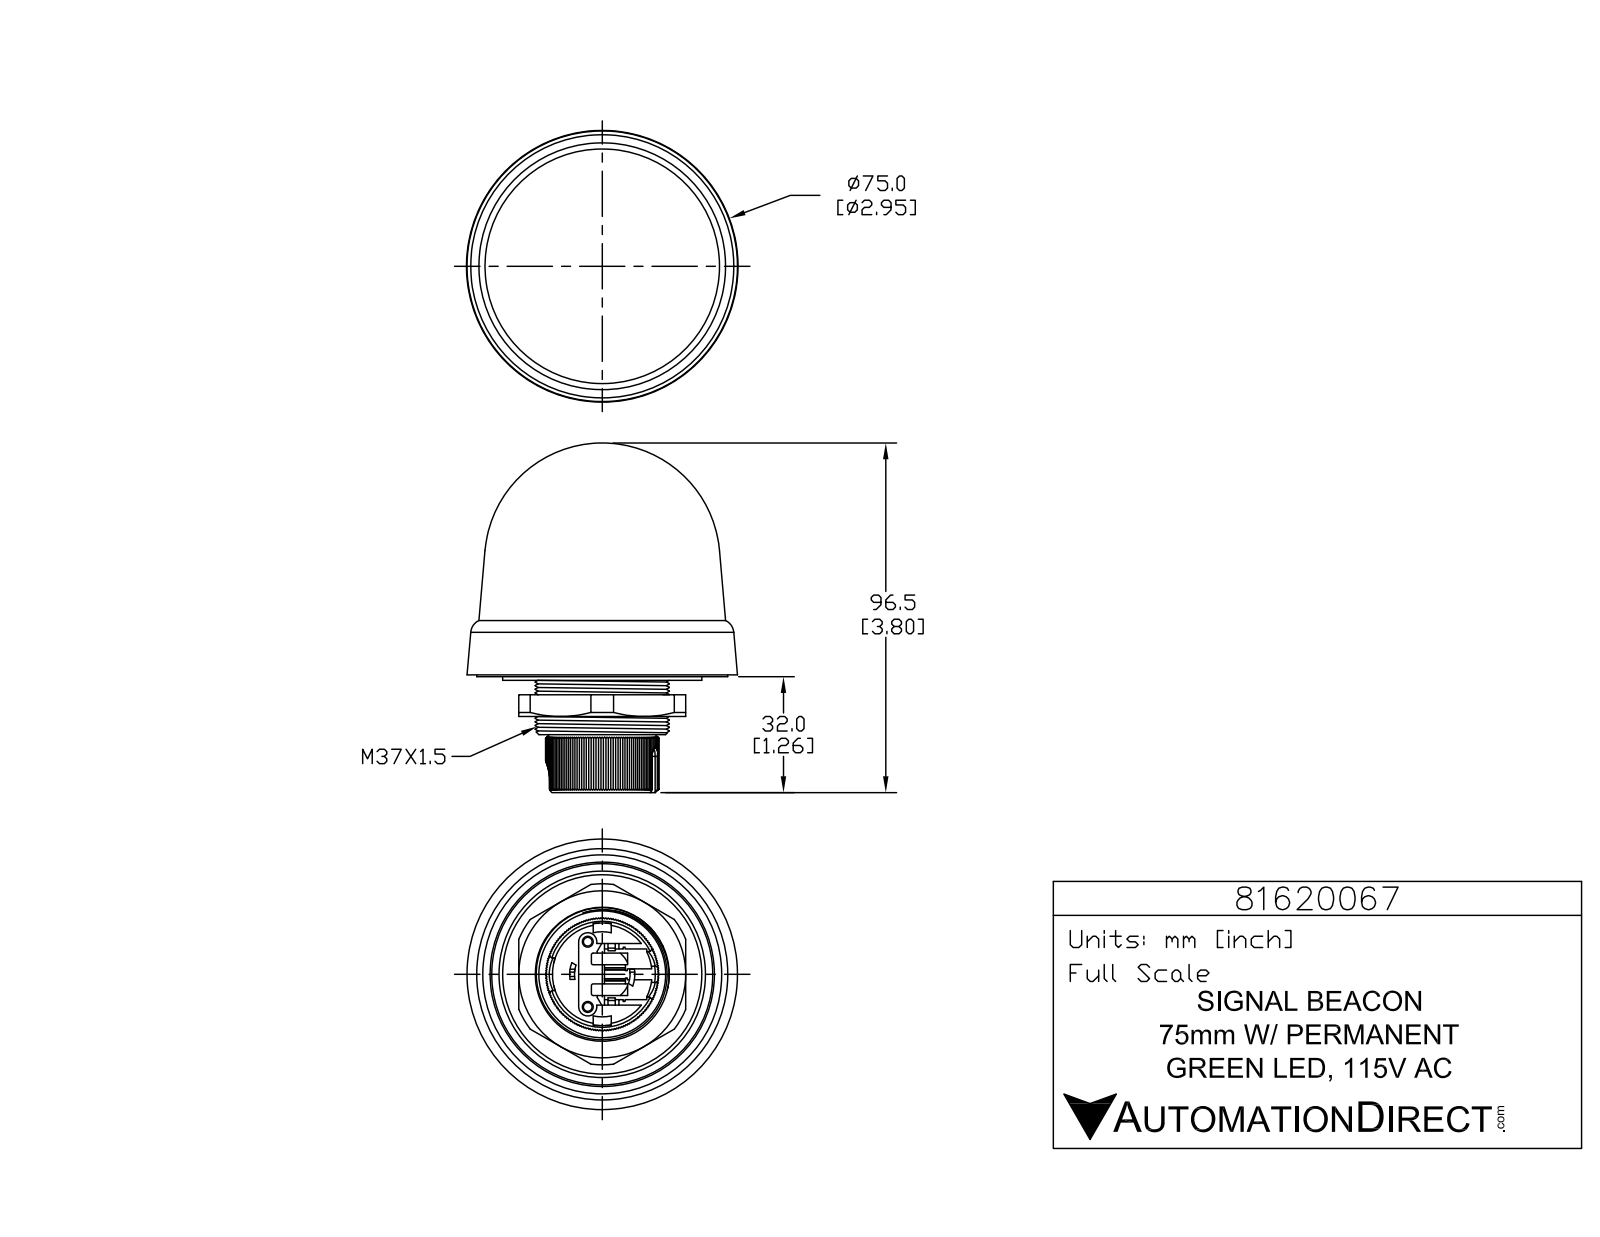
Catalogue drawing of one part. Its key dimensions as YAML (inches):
part_name: "81620067"
step_written_by: "SolidWorks 2019 (CONFIG_CONTROL_DESIGN)"
units: inches
bodies: {solids: 3, faces: 560, planar: 432, cylindrical: 80, other: 48}
overall_size: [3.799, 2.941, 2.941]
volume: 12.36
surface_area: 58.68
round_holes:
  - {diameter: 0.094, count: 2}
  - {diameter: 0.118, count: 2}
  - {diameter: 0.604, count: 1}
  - {diameter: 1.142, count: 1}
round_bosses_or_shafts:
  - {diameter: 0.217, count: 2}
  - {diameter: 0.067, count: 2}
  - {diameter: 2.165, count: 1}
  - {diameter: 1.457, count: 1}
  - {diameter: 0.925, count: 1}
partial_cylinders:
  - {radius: 0.008, count: 6}
  - {radius: 0.039, count: 6}
  - {radius: 0.02, count: 4}
  - {radius: 0.031, count: 2}
  - {radius: 0.079, count: 2}
  - {radius: 0.098, count: 2}
  - {radius: 0.177, count: 1}
  - {radius: 0.354, count: 1}
face_to_face_distances: [0.177, 0.354, 0.197, 0.433, 0.512, 0.335, 0.059, 0.394, 0.118, 0.157]
hole_center_spacings: [0.388, 0.709]
